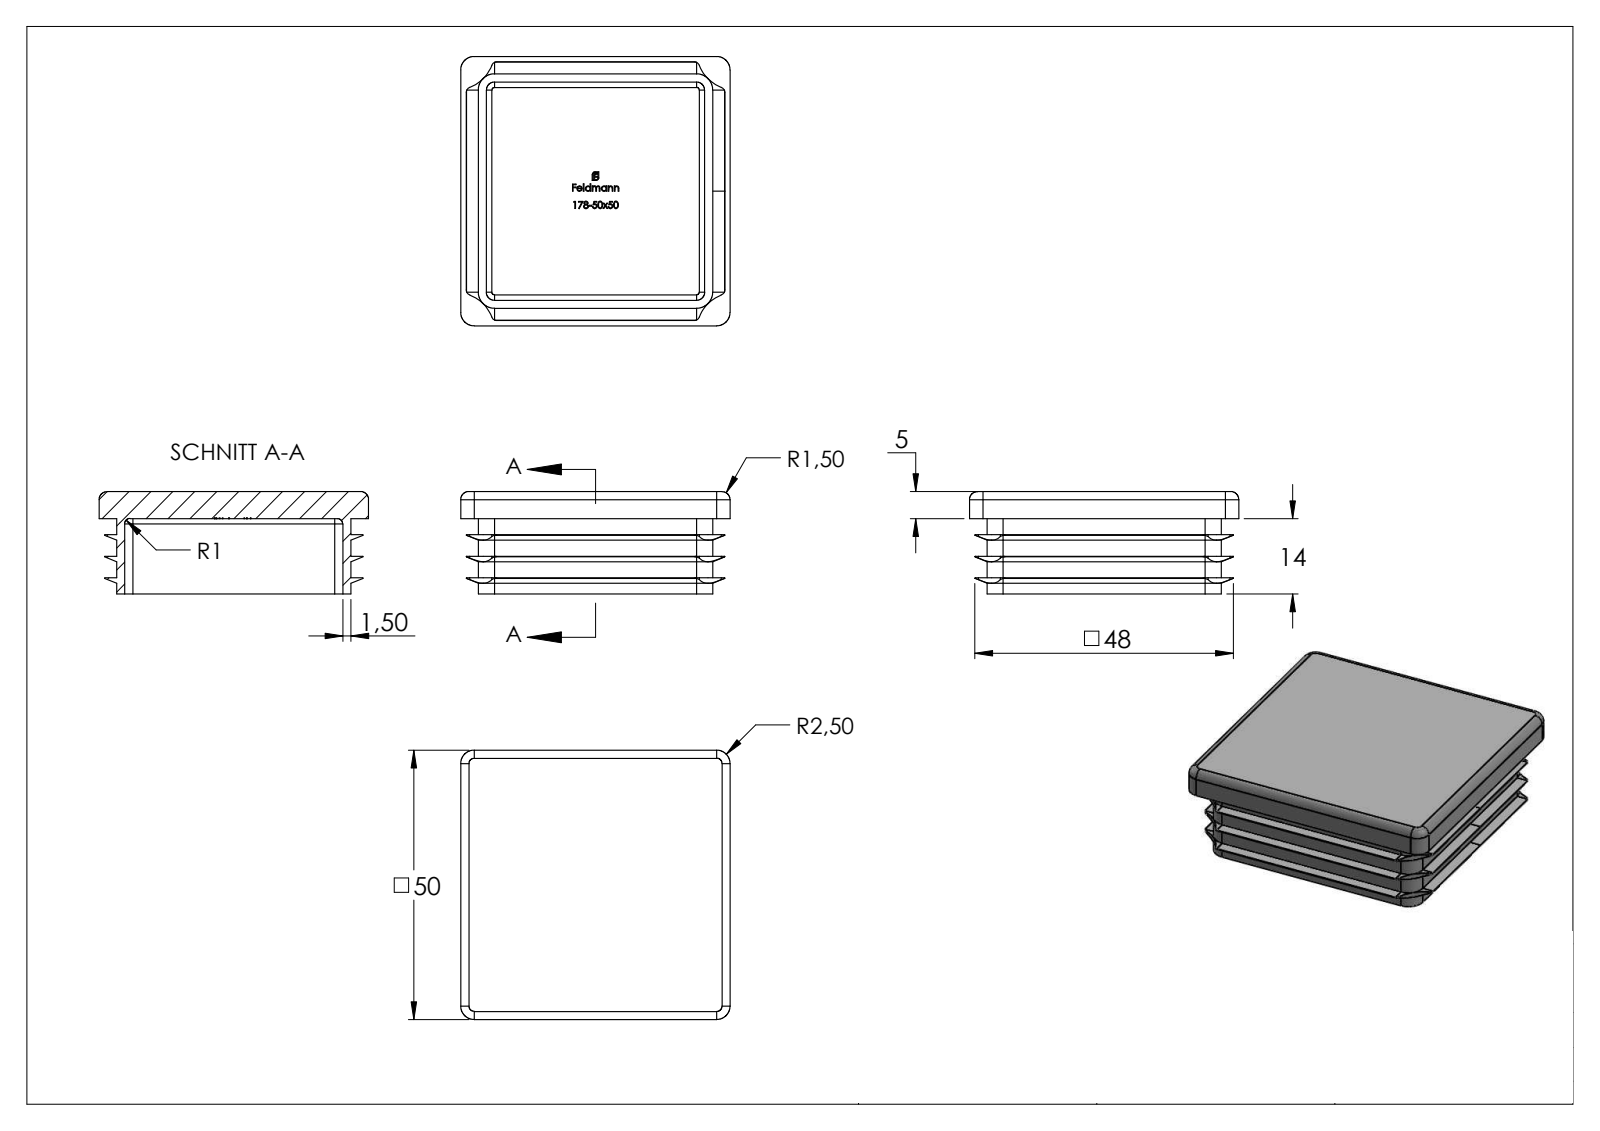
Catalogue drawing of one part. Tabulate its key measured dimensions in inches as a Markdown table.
| quantity | value |
| --- | --- |
| part name | 178-50x50 |
| STEP written by | SolidWorks 2018 (CONFIG_CONTROL_DESIGN) |
| units | inches |
| bodies | 1 solid, 465 faces (235 planar, 83 cylindrical, 147 other) |
| overall size | 1.969 × 1.969 × 0.748 |
| volume | 1.003 in³ |
| surface area | 18.84 in² |
| partial cylindrical surfaces (radius × count) | 0.039 × 12, 0.059 × 8, 0.098 × 4, 0.118 × 4, 0.276 × 4 |
| main face-to-face distances | 0.197, 0.059, 1.654, 1.594, 1.713, 0.157, 0.315, 0.128, 0.187, 1.781 |
